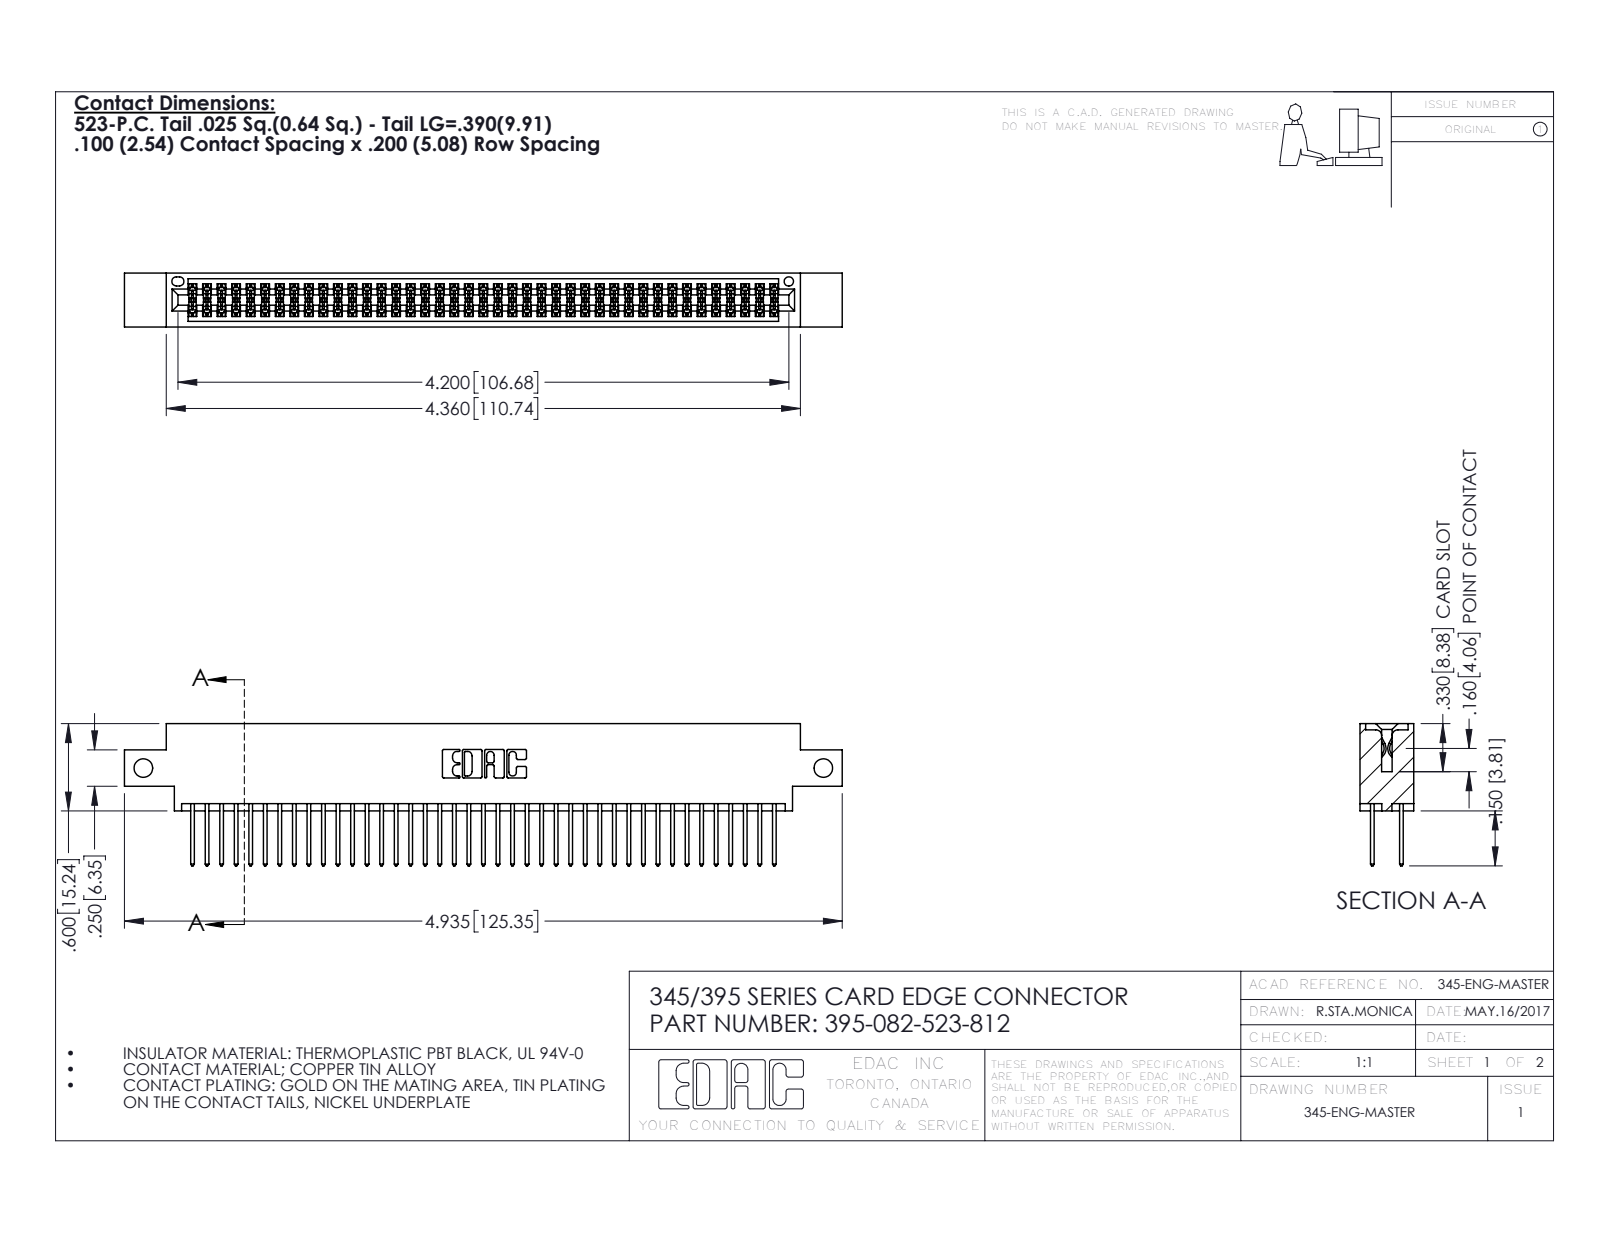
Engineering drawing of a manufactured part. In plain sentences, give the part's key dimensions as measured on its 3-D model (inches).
The part is named "345 Part_0.170 Offset - Side Mount; 345-292-001_345-293-123; 395-082-523-812". Its 3-D file was written by "SolidWorks 2016 (CONFIG_CONTROL_DESIGN)". It is 83 solids with 4230 faces: 2790 planar, 1440 cylindrical and 0 other. Overall it measures 4.935 by 0.977 by 0.37 inches. Its volume is 0.741 cubic inches and its surface area 28.95 square inches. Round holes: 2 of diameter 0.128, 1 of diameter 0.064. Partial cylindrical surfaces (rounded edges, fillets, slot ends): 123 of radius 0.006, 82 of radius 0.01, 22 of radius 0.01, 6 of radius 0.007, 6 of radius 0.031, 3 of radius 0.026, 2 of radius 0.014, 2 of radius 0.019. The main face-to-face distances are 0.298, 0.072, 0.2, 0.098, 0.272, 0.025, 0.37, 0.225, 0.175, 0.149. The hole center spacings are 4.675.
